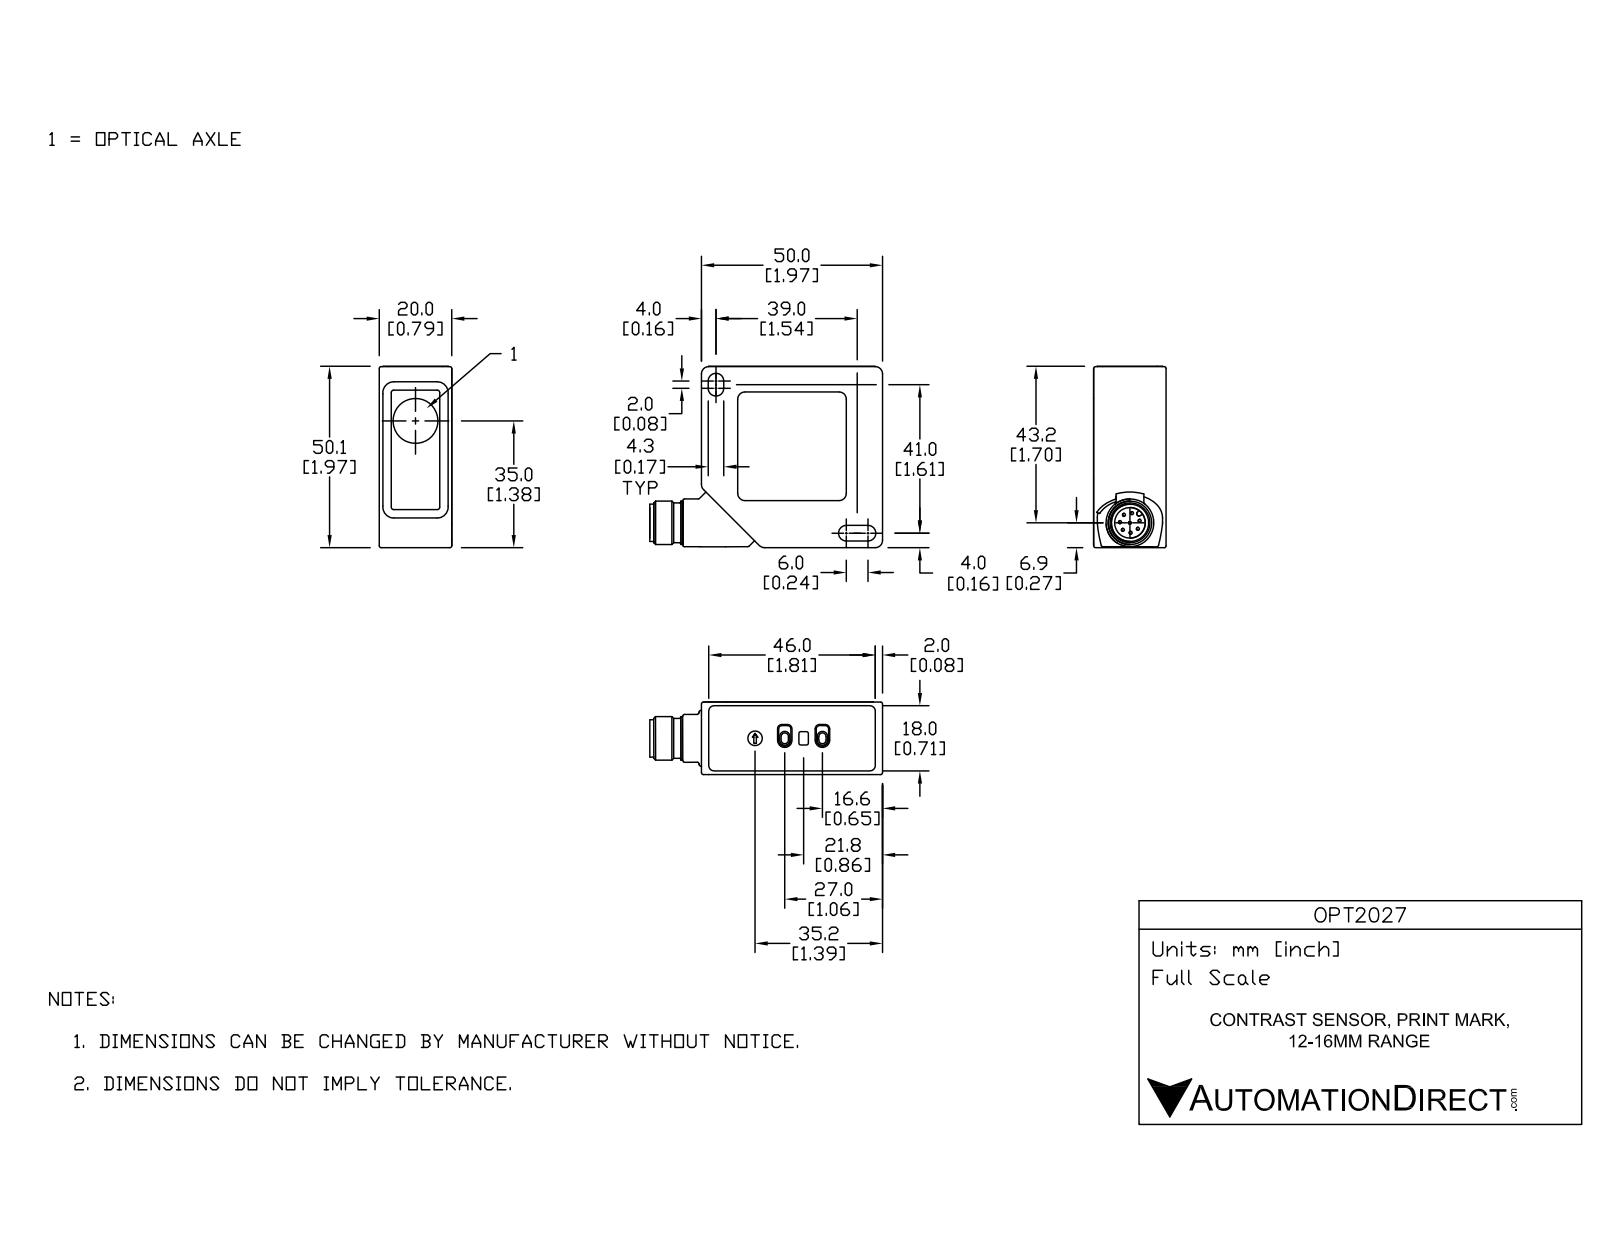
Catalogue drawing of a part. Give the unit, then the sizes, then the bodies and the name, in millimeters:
Units: millimetres
Overall size (bounding box): 64.29 × 50.1 × 20.05
Round holes (diameter × count): ⌀4 ×1, ⌀8.45 ×1
Round bosses / shafts (diameter × count): ⌀0.82 ×8, ⌀18 ×1, ⌀13.2 ×1, ⌀12 ×1, ⌀11 ×1, ⌀10.3 ×1
Partial cylindrical surfaces — rounded edges, fillets, slot ends (radius × count): R0.5 ×19, R2 ×11, R0.25 ×9, R1.5 ×8, R1.6 ×7, R0.3 ×6, R0.7 ×4, R1 ×4
Main face-to-face distances: 20.05, 50.1, 50, 1.6, 48.4, 20, 4.3, 1.85, 6.15, 19.85
Volume: 48 553 mm³ · Surface area: 11 143 mm²
Bodies: 1 solid, 496 faces (217 planar, 152 cylindrical, 127 other)
Part name (STEP PRODUCT): ZNR11793A-2A
STEP written by: Unknown (automotive_design)
